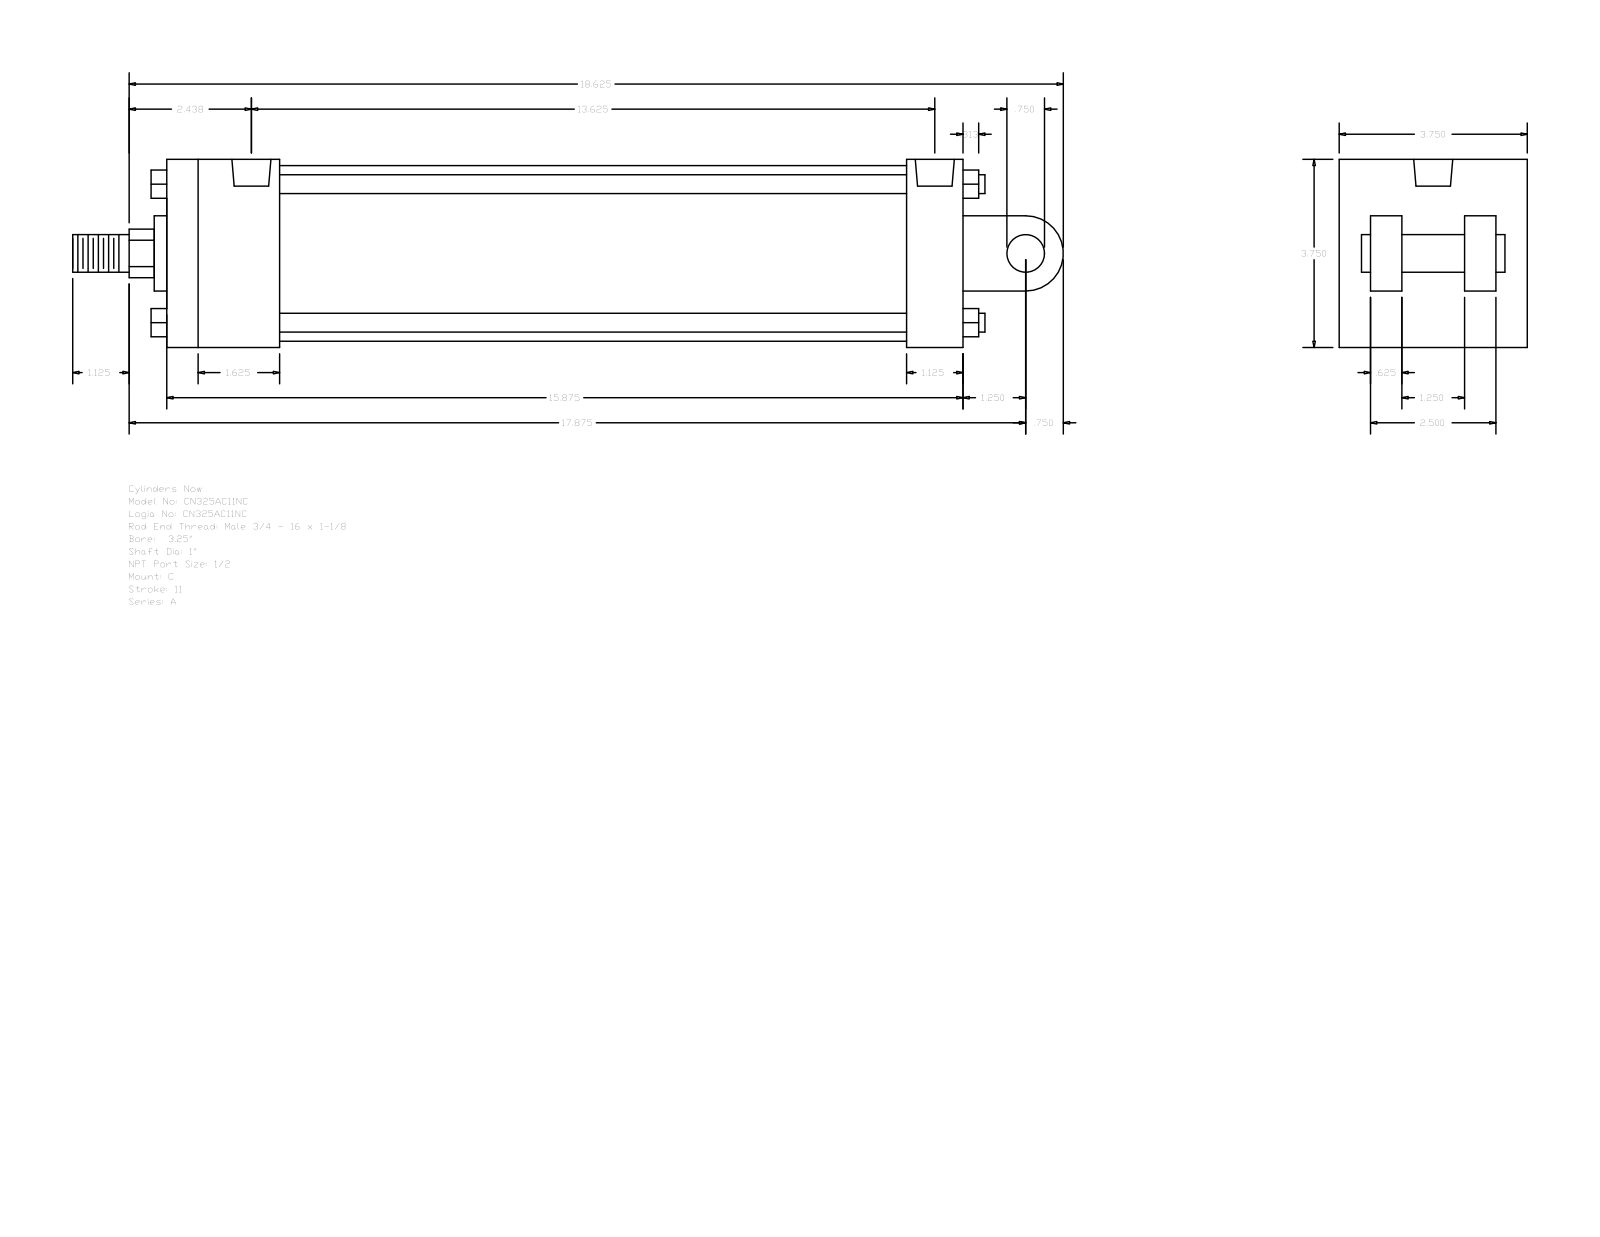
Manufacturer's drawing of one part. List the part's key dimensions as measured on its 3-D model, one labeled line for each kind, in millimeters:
Part name (STEP PRODUCT): A_C__0325_1
STEP written by: GSSL Pune (CONFIG_CONTROL_DESIGN)
Units: millimetres
Bodies: 0 solids, 135 faces (102 planar, 33 cylindrical, 0 other)
Overall size (bounding box): 501.65 × 95.25 × 95.25
Round holes (diameter × count): ⌀8.73 ×4, ⌀19.77 ×2
Round bosses / shafts (diameter × count): ⌀9.53 ×4, ⌀19.05 ×2, ⌀88.9 ×1, ⌀38.1 ×1, ⌀25.4 ×1
Partial cylindrical surfaces — rounded edges, fillets, slot ends (radius × count): R12.29 ×1, R19.05 ×1
Main face-to-face distances: 95.24, 403.22, 15.87, 63.5, 28.57, 79.37, 31.74, 47.63, 66.67, 374.65
Hole centre spacings: 3.18, 339.72, 342.9, 346.08
